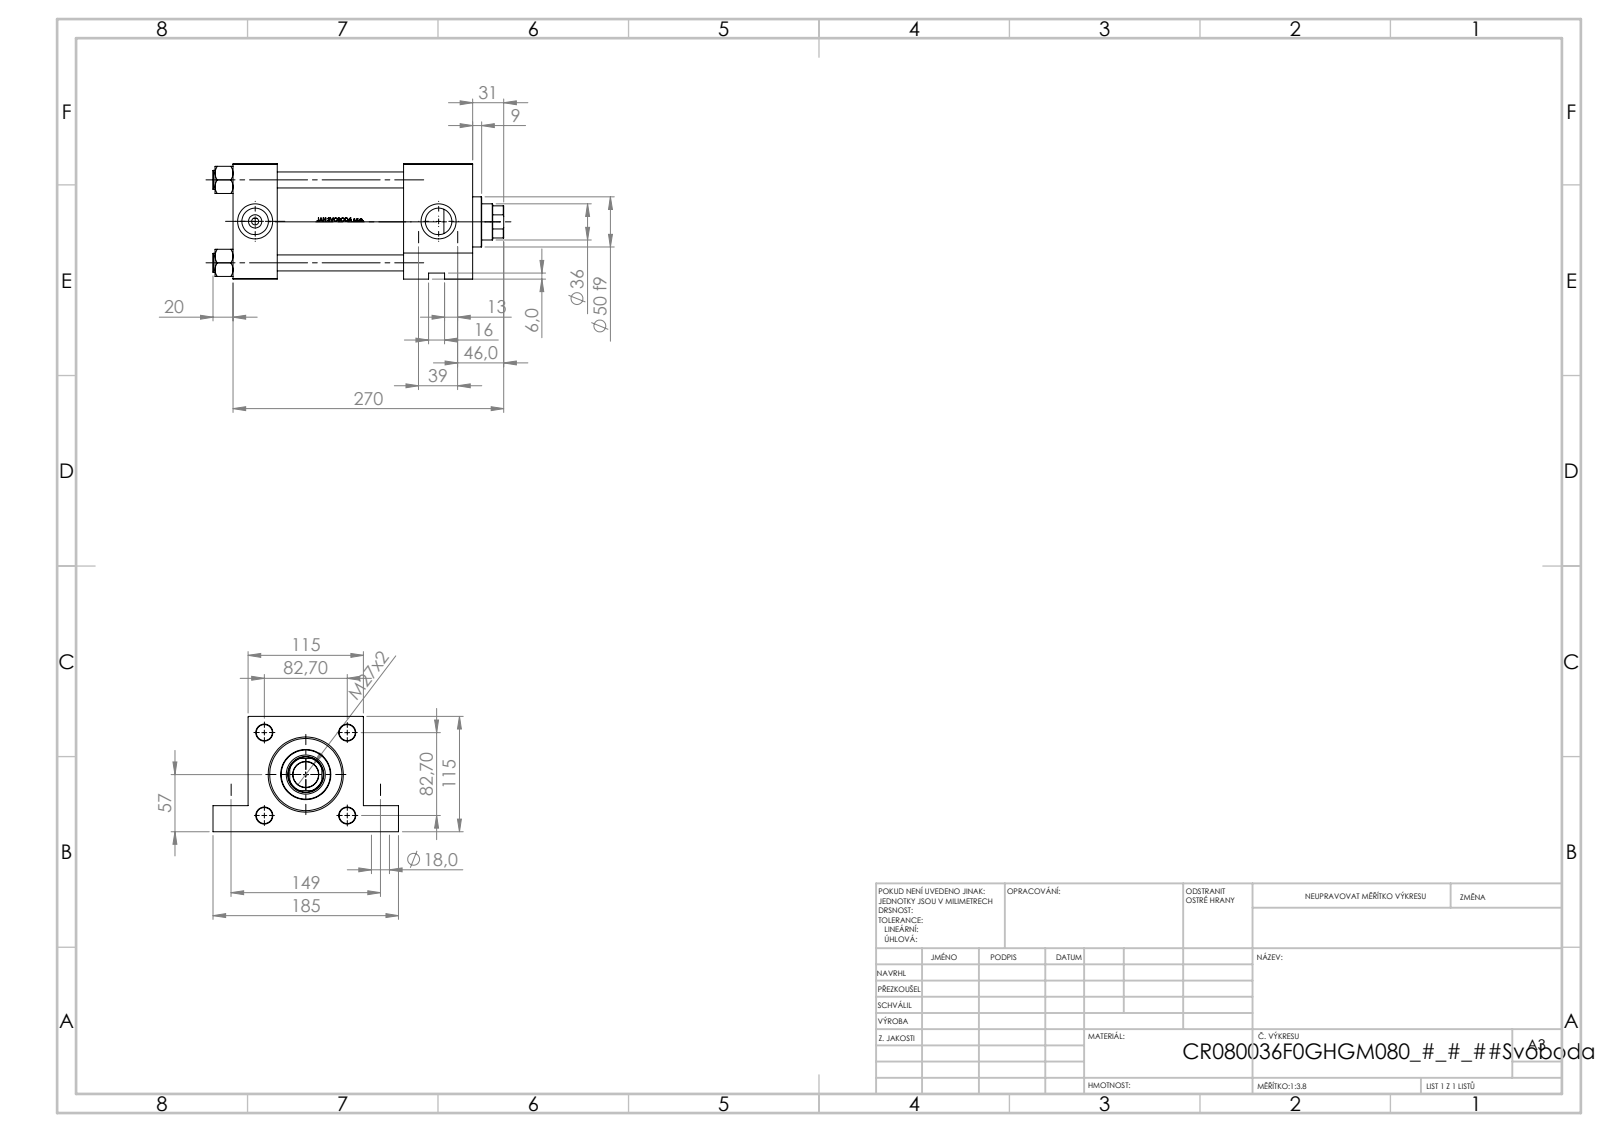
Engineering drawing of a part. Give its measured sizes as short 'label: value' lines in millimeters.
name: V215_VC_A; V215CR_F_TYCINKA; V215CR_F_Body; NUT_M5_F (+1 more)
written by: SolidWorks 2019 (CONFIG_CONTROL_DESIGN)
unit: mm
bodies: 11 solids, 1151 faces (485 planar, 126 cylindrical, 540 other)
size: 290 × 185 × 115
volume: 2 039 000 mm³; area: 333 717 mm²
holes: 4× ⌀16, 4× ⌀18, 2× ⌀7, 2× ⌀26.44, 2× ⌀35, 1× ⌀25.5, 1× ⌀36, 1× ⌀39, 1× ⌀61, 1× ⌀72, 1× ⌀80
bosses: 4× ⌀19, 1× ⌀86, 1× ⌀50
rounds: 1× R17.5
face distances: 115, 44, 195, 239, 170, 126, 69, 210.3, 166.3, 40.3
hole spacings: 82.7, 39, 58.13, 58.83, 116.96, 149, 154.02, 183
